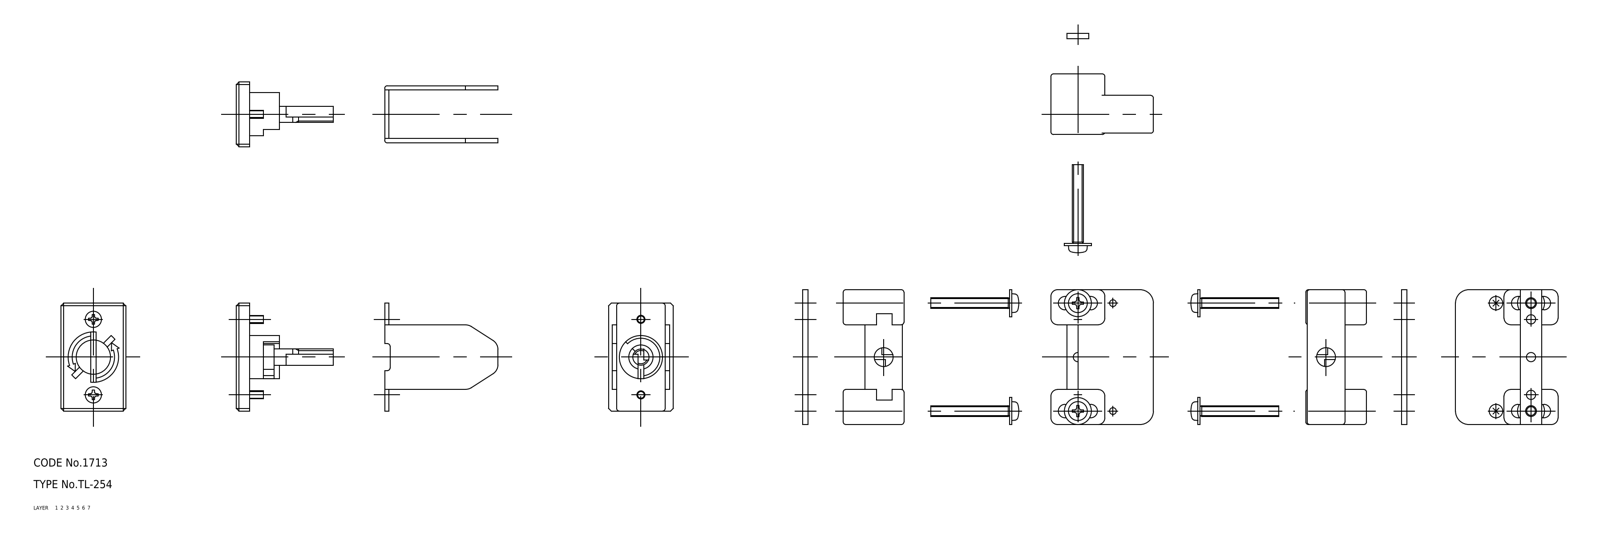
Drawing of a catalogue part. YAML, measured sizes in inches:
part_name: "screw_A; screw_B; plate; holder (+2 more)"
step_written_by: "CADfix (AUTOMOTIVE_DESIGN)"
units: inches
bodies: {solids: 8, faces: 432, planar: 0, cylindrical: 0, other: 432}
overall_size: [5.356, 1.969, 1.327]
volume: 2.123
surface_area: 32.09
